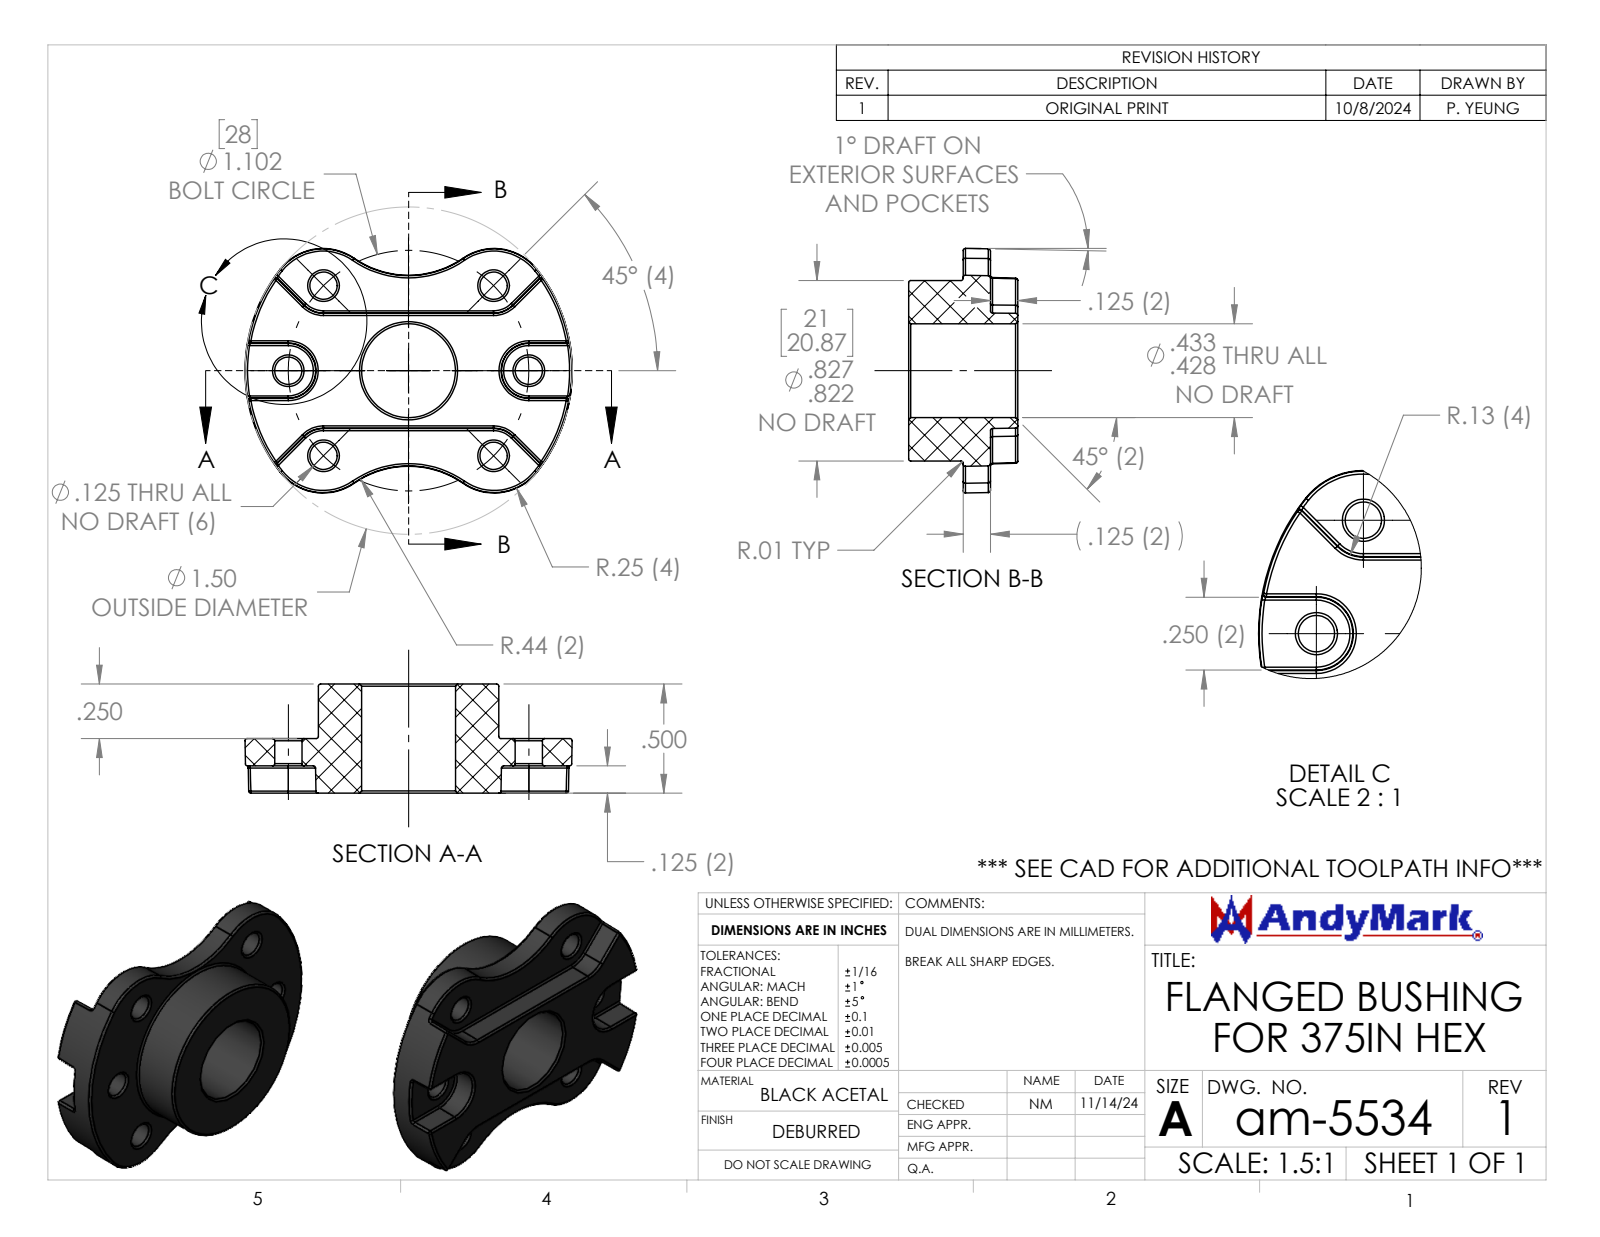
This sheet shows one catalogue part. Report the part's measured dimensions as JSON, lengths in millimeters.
{"part_name": "am-5534 0.430x21mm OD NeveRest Pattern Flanged Bushing for 0.375IN Hex", "step_written_by": "SolidWorks 2024 (AUTOMOTIVE_DESIGN)", "units": "millimeters", "bodies": {"solids": 1, "faces": 169, "planar": 17, "cylindrical": 36, "other": 116}, "overall_size": [38.1, 28.4, 12.7], "volume_mm3": 5160, "surface_area_mm2": 3277, "round_holes": [[3.2, 5], [3.2, 1], [10.9, 1]], "round_bosses_or_shafts": [[21, 1]], "partial_cylinders_radius": [[0.3, 16]], "face_to_face_distances": [6.4, 3.2, 3.2, 9.5, 12.7, 9.9], "hole_center_spacings": [14, 10.7, 19.8, 25.9, 28]}
